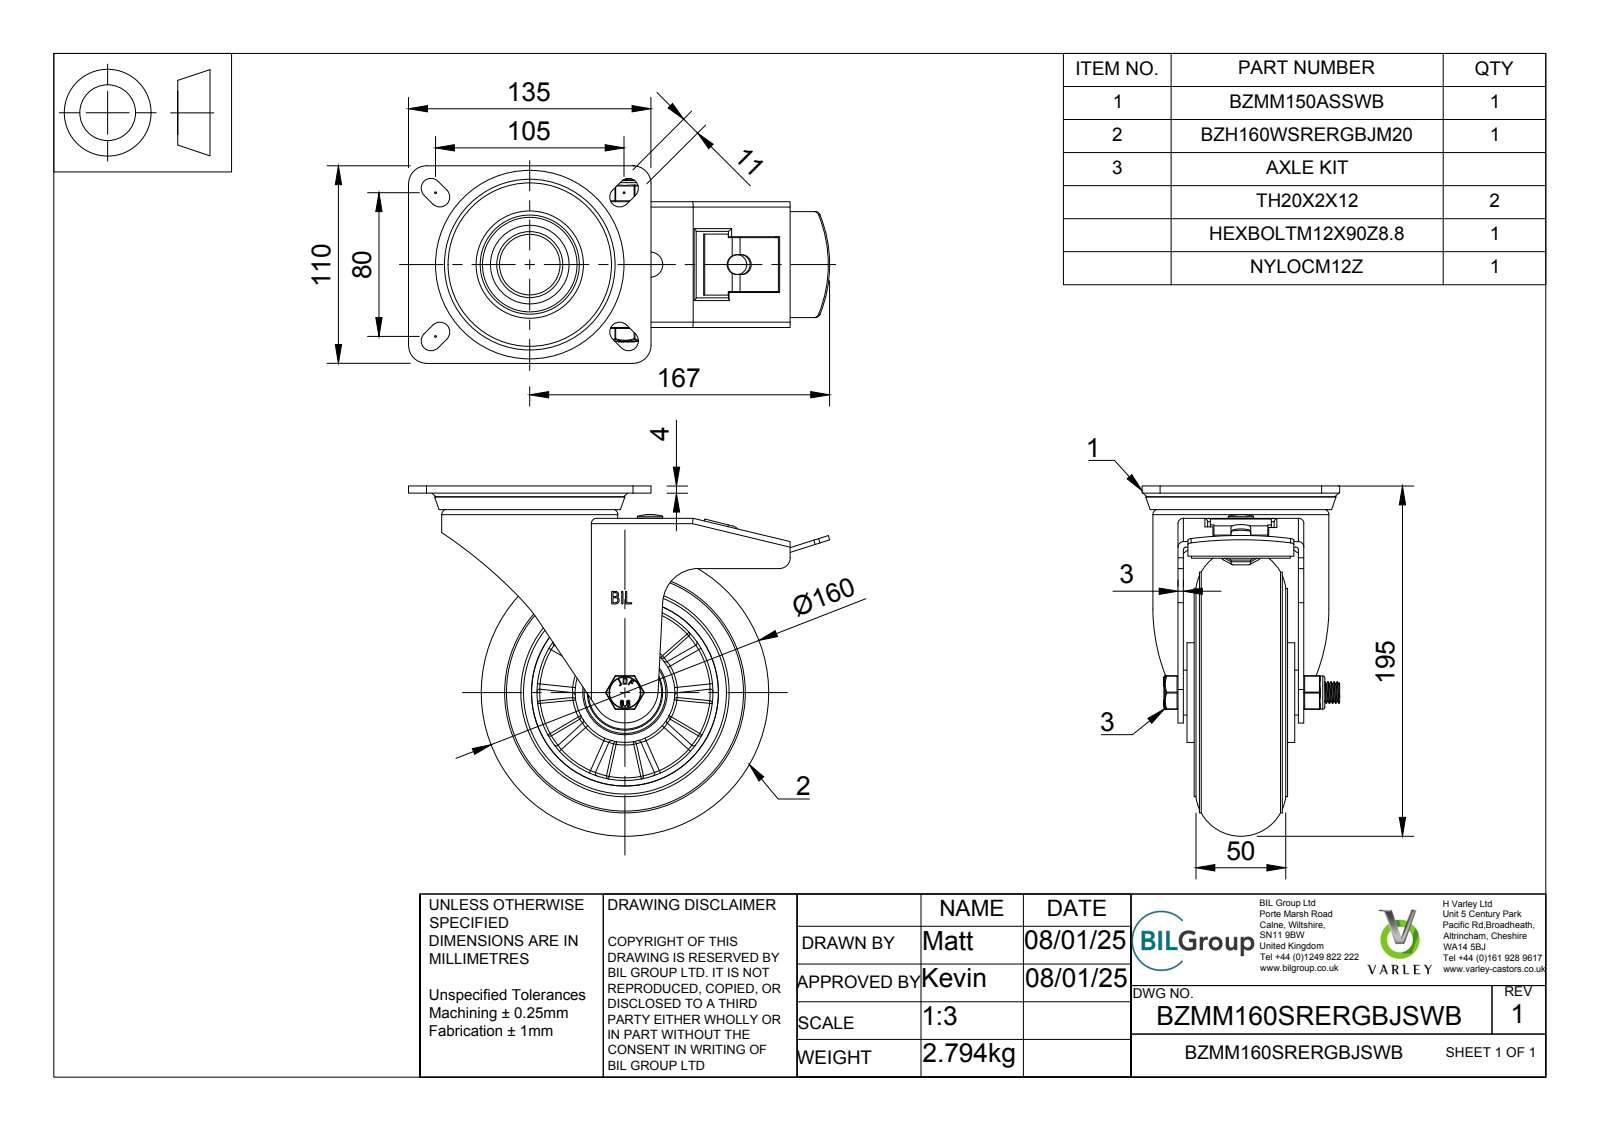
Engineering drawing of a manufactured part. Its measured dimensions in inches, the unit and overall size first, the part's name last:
Units: inches
Overall size (bounding box): 9.232 × 7.677 × 4.331
Round holes (diameter × count): ⌀0.315 ×1, ⌀0.433 ×1, ⌀0.472 ×1, ⌀0.48 ×1, ⌀0.551 ×1, ⌀0.787 ×1, ⌀1.122 ×1, ⌀1.213 ×1, ⌀1.329 ×1, ⌀1.565 ×1, ⌀1.587 ×1, ⌀1.594 ×1
Round bosses / shafts (diameter × count): ⌀5.276 ×1, ⌀4.567 ×1, ⌀3.858 ×1, ⌀3.071 ×1, ⌀2.185 ×1, ⌀1.969 ×1, ⌀1.606 ×1, ⌀1.232 ×1
Partial cylindrical surfaces — rounded edges, fillets, slot ends (radius × count): R0.02 ×20, R0.059 ×10, R0.217 ×10, R0.01 ×6, R0.098 ×6, R0.118 ×6, R0.019 ×4, R0.035 ×4
Main face-to-face distances: 0.118, 0.354, 0.197, 0.276, 0.157, 0.472, 0.079, 0.669, 2.638, 0.551
Hole centre spacings: 2.638
Volume: 51.83 in³ · Surface area: 494.7 in²
Bodies: 82 solids, 1527 faces (568 planar, 262 cylindrical, 697 other)
Part name (STEP PRODUCT): BZMM160SRERGBJSWB v3; BZMM150ASSWB - 64 v1; ZINC PLATED, PRESSED STEEL TOP PLATE; ZINC PLATED, PRESSED STEEL TOP PLATE Geometry (+7 more)
STEP written by: Autodesk Translation Framework v13.20.0.188 (AP242_MANAGED_MODEL_BASED_3D_ENGINEERING_MIM_LF)
